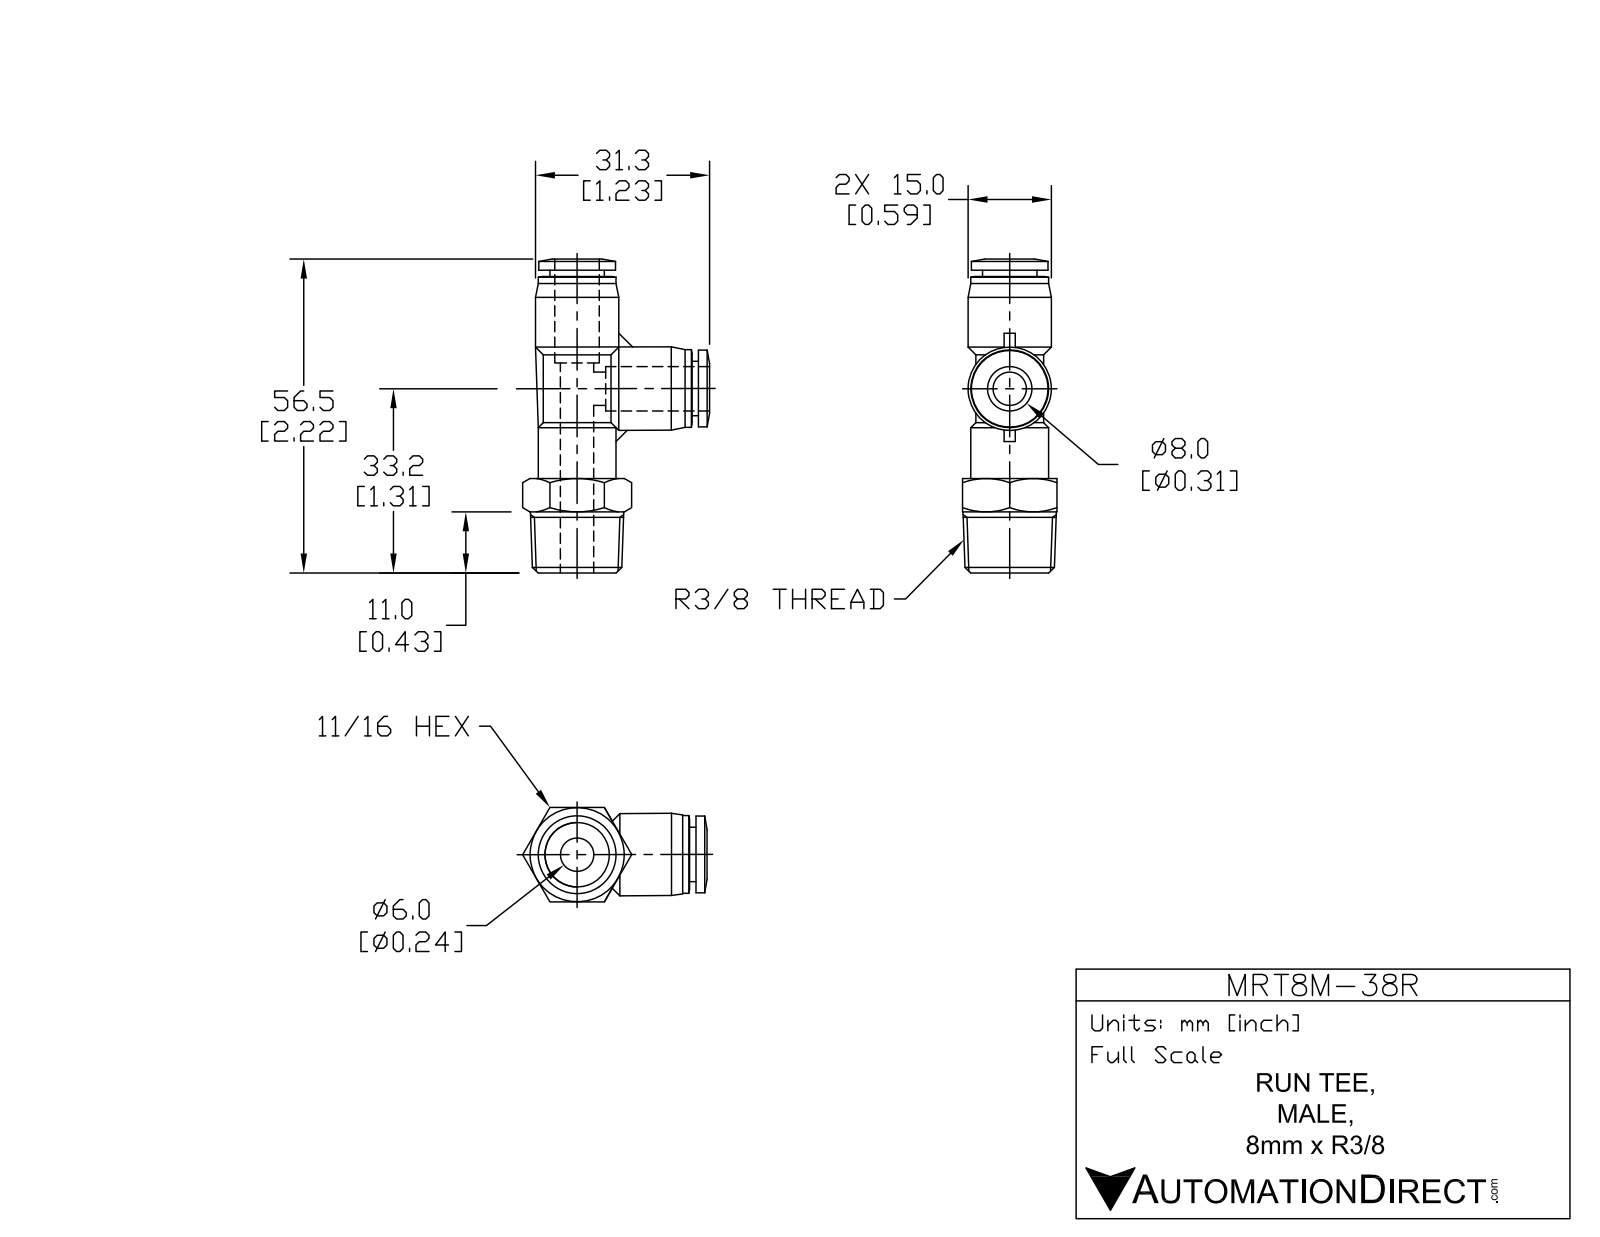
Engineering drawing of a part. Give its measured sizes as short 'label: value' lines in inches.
name: MRT8M-38R
written by: SolidWorks 2015 (AUTOMOTIVE_DESIGN)
unit: in
bodies: 1 solid, 102 faces (25 planar, 34 cylindrical, 43 other)
size: 2.209 × 1.306 × 0.669
volume: 0.564 in³; area: 9.021 in²
holes: 2× ⌀0.236, 2× ⌀0.327
bosses: 2× ⌀0.591, 2× ⌀0.551, 2× ⌀0.543, 2× ⌀0.48, 2× ⌀0.386
face distances: 0.669, 0.045, 2.13, 1.461, 0.596, 0.642, 2.085, 1.415, 0.295, 0.374
